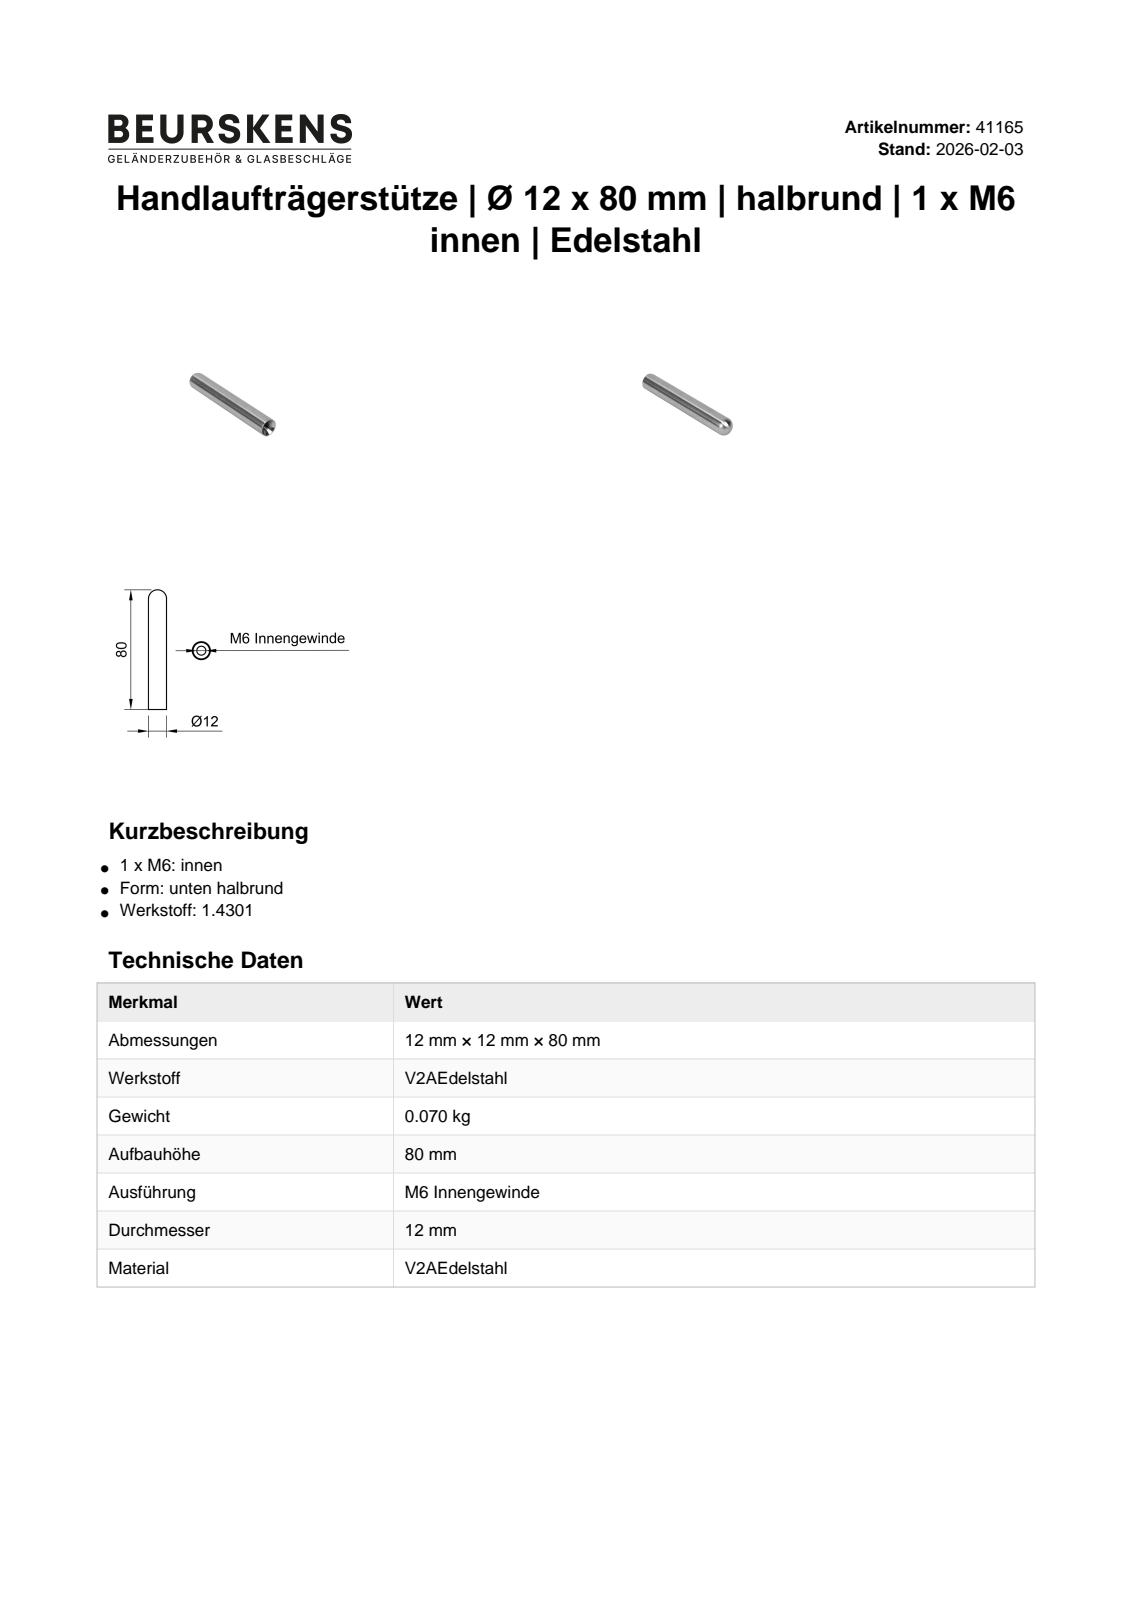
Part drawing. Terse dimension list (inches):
name: 41165
written by: Autodesk Inventor 2022 (AUTOMOTIVE_DESIGN)
unit: in
bodies: 1 solid, 6 faces (2 planar, 2 cylindrical, 2 other)
size: 3.15 × 0.472 × 0.472
volume: 0.504 in³; area: 5.317 in²
holes: 1× ⌀0.236
bosses: 1× ⌀0.472
face distances: 0.669
